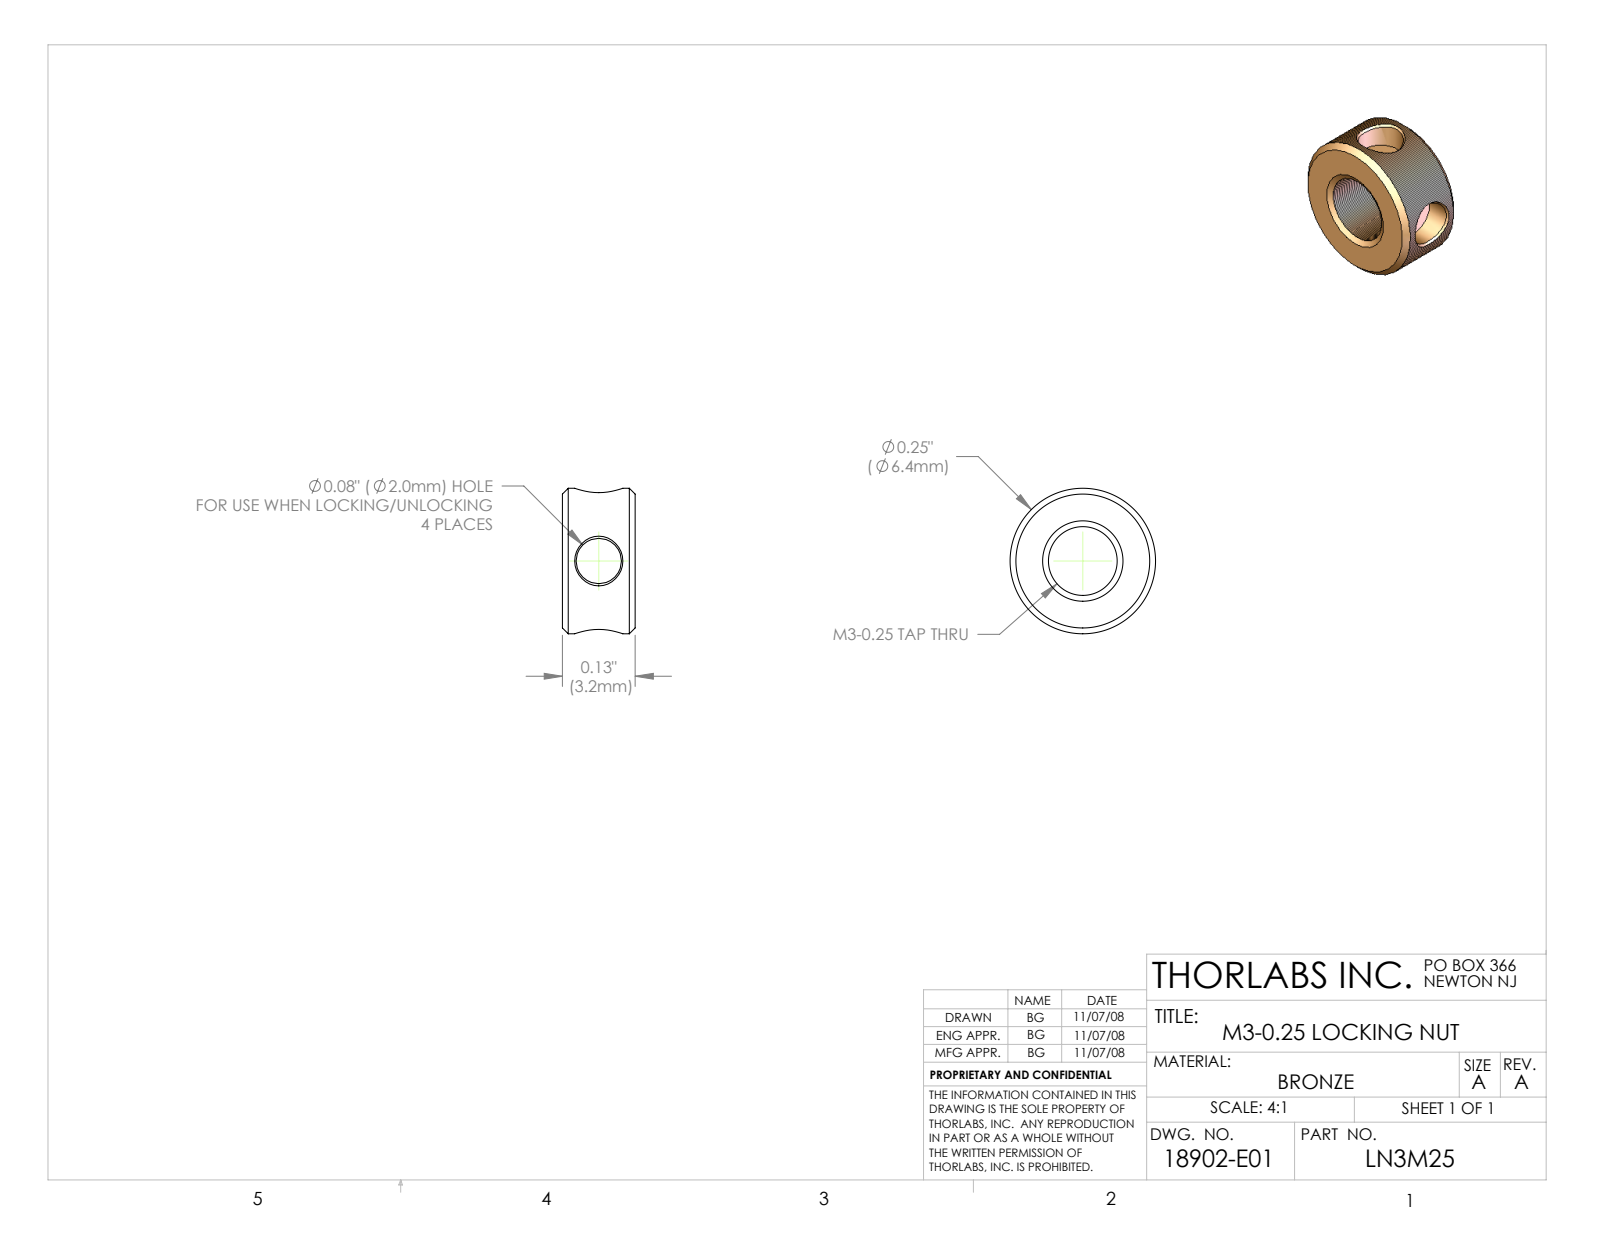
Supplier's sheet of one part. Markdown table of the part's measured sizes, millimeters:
| quantity | value |
| --- | --- |
| part name | 18902-E0W |
| STEP written by | SolidWorks 2007 (AUTOMOTIVE_DESIGN) |
| units | millimeters |
| bodies | 1 solid, 34 faces (6 planar, 12 cylindrical, 16 other) |
| overall size | 6.35 × 6.35 × 3.17 |
| volume | 63 mm³ |
| surface area | 159 mm² |
| round holes (diameter × count) | 1.98 × 2, 3 × 1 |
| round bosses / shafts (diameter × count) | 6.35 × 1 |
| main face-to-face distances | 3.18, 4.06 |
